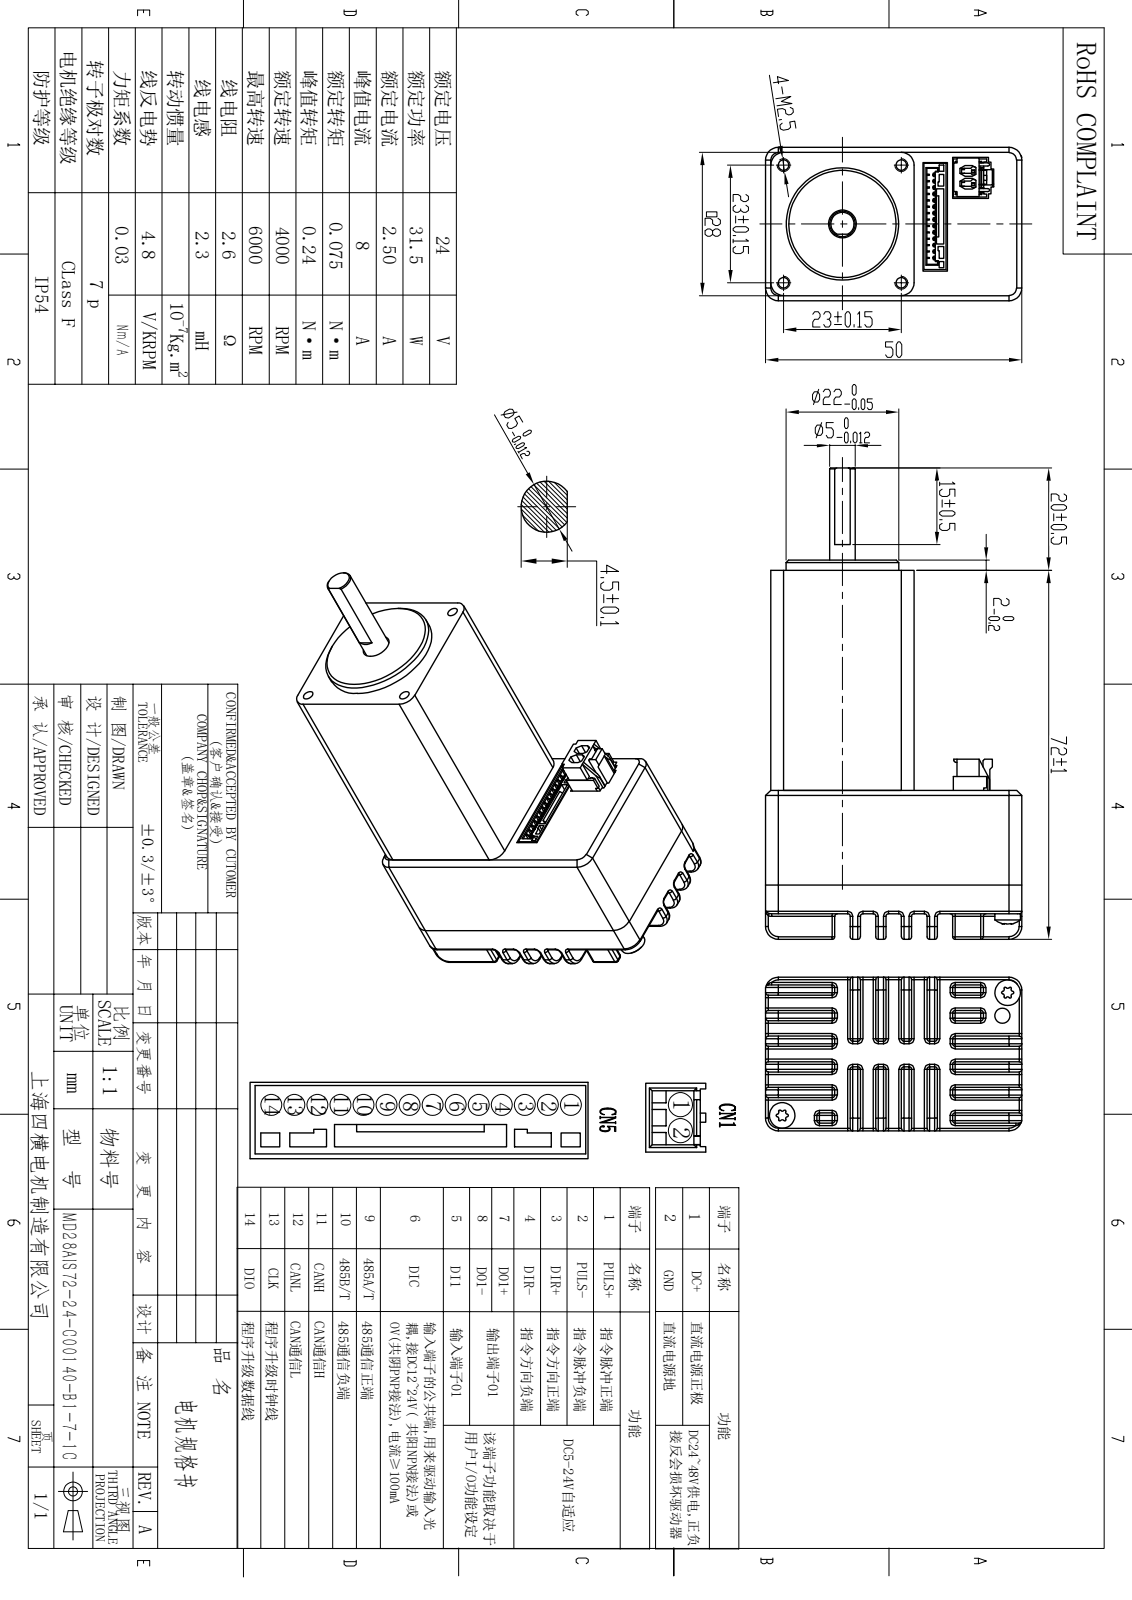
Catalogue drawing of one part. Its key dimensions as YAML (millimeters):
part_name: "MD28AIS72-24-C00140-B1-7-1C"
step_written_by: "SolidWorks 2020 (CONFIG_CONTROL_DESIGN)"
units: millimeters
bodies: {solids: 10, faces: 1293, planar: 681, cylindrical: 404, other: 208}
overall_size: [92.1, 50, 30]
volume: 32608
surface_area: 30071
round_holes:
  - {diameter: 2.05, count: 10}
  - {diameter: 3, count: 3}
  - {diameter: 1.5, count: 2}
  - {diameter: 1.6, count: 2}
  - {diameter: 2.6, count: 2}
  - {diameter: 5, count: 1}
  - {diameter: 5.5, count: 1}
  - {diameter: 9, count: 1}
  - {diameter: 18, count: 1}
  - {diameter: 22, count: 1}
  - {diameter: 24.5, count: 1}
  - {diameter: 25, count: 1}
round_bosses_or_shafts:
  - {diameter: 5, count: 3}
  - {diameter: 2.5, count: 2}
  - {diameter: 2.17, count: 2}
  - {diameter: 13, count: 1}
  - {diameter: 11.6, count: 1}
  - {diameter: 8, count: 1}
partial_cylinders:
  - {radius: 0.5, count: 135}
  - {radius: 1, count: 28}
  - {radius: 0.23, count: 12}
  - {radius: 0.37, count: 12}
  - {radius: 2.5, count: 12}
  - {radius: 0.3, count: 6}
  - {radius: 0.4, count: 6}
  - {radius: 1.5, count: 4}
face_to_face_distances: [1, 28, 2, 29, 5, 1.5, 3, 30, 10, 4.5]
hole_center_spacings: [22.13, 1.26, 15, 16.26, 21.22, 23, 31.27, 0.56]
